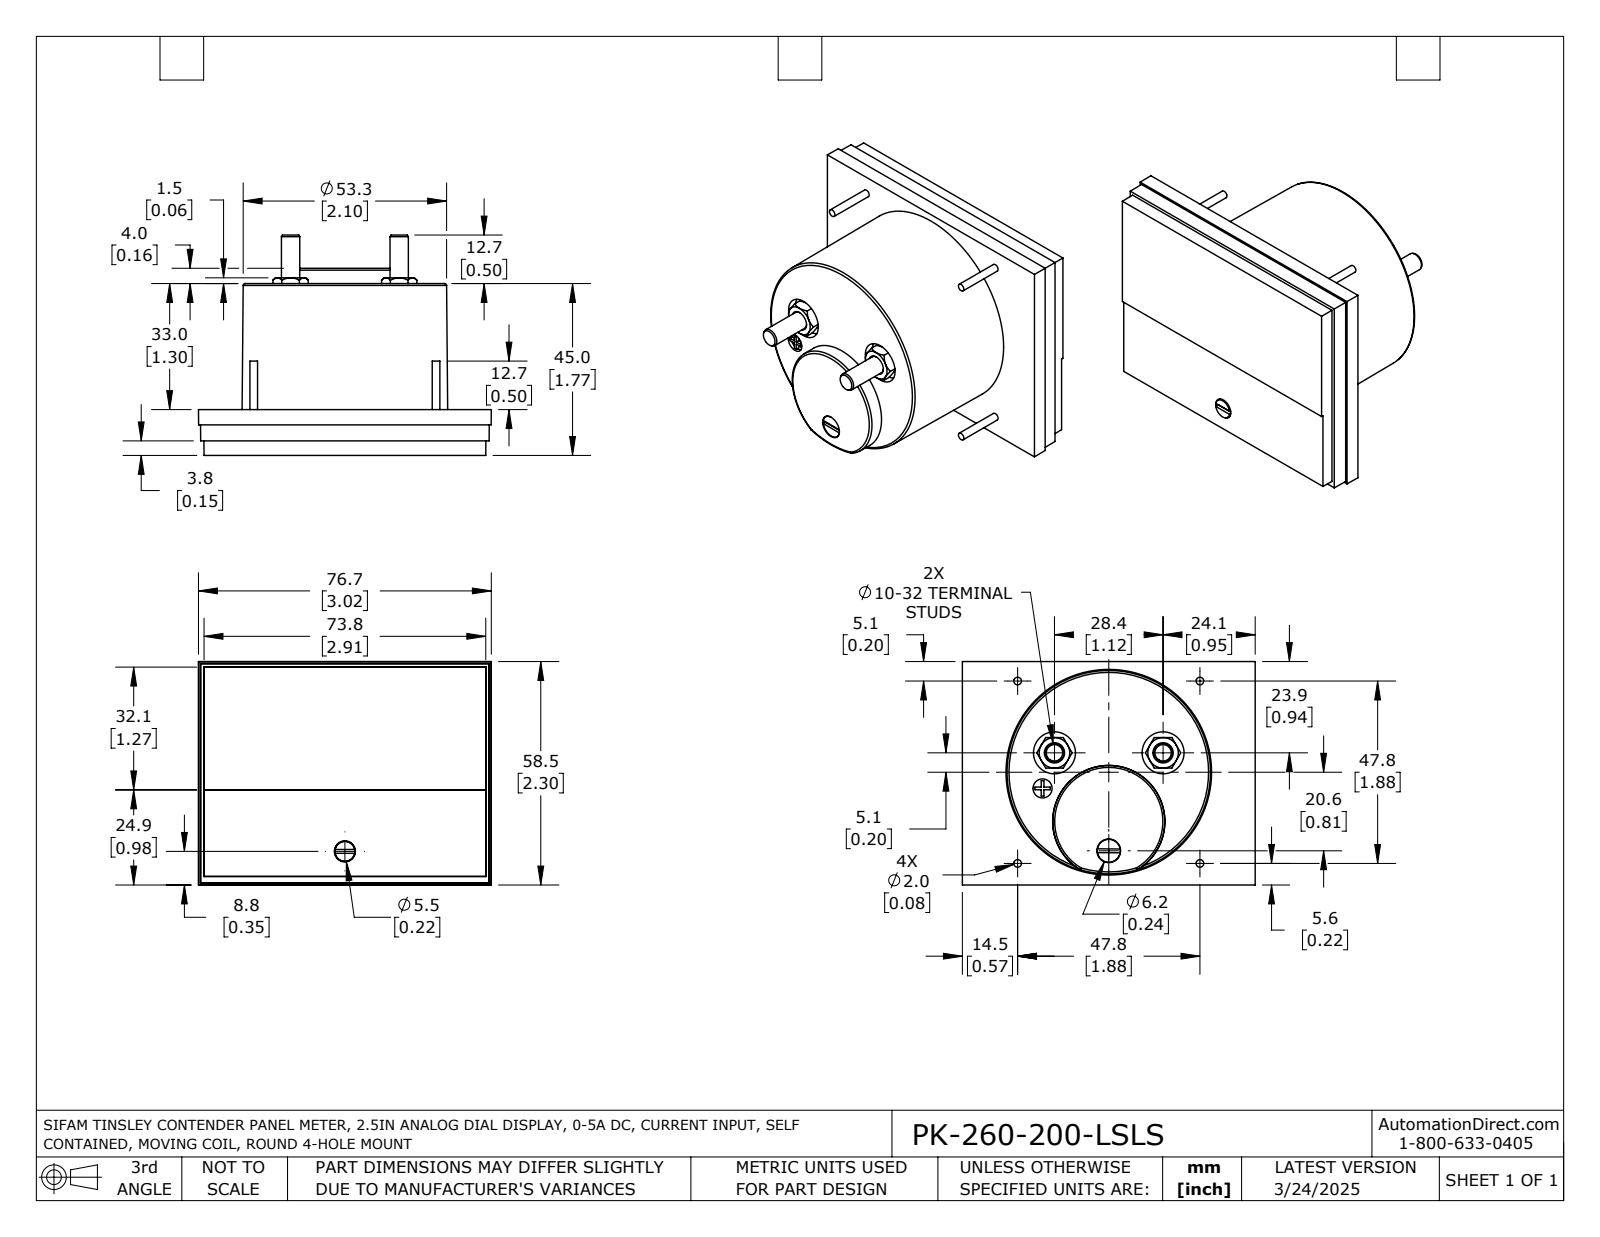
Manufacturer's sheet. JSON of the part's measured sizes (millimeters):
{"part_name": "PK-260-200-LSLS", "step_written_by": "SolidWorks 2021 (AUTOMOTIVE_DESIGN)", "units": "millimeters", "bodies": {"solids": 1, "faces": 192, "planar": 95, "cylindrical": 37, "other": 60}, "overall_size": [76.7, 58.5, 57.7], "volume_mm3": 125500, "surface_area_mm2": 23580, "round_holes": [[5, 3], [11, 2], [5.3, 1], [5.5, 1], [6.2, 1]], "round_bosses_or_shafts": [[2, 4], [4.8, 2], [6, 1], [5.2, 1]], "partial_cylinders_radius": [[0.8, 1]], "face_to_face_distances": [0.5, 12, 3.3, 8.2, 3.8, 11.5, 1.4, 2, 10.1, 1.9], "hole_center_spacings": [29.3, 29.5, 9.8, 23.8, 23.9, 28.4, 32.9]}
